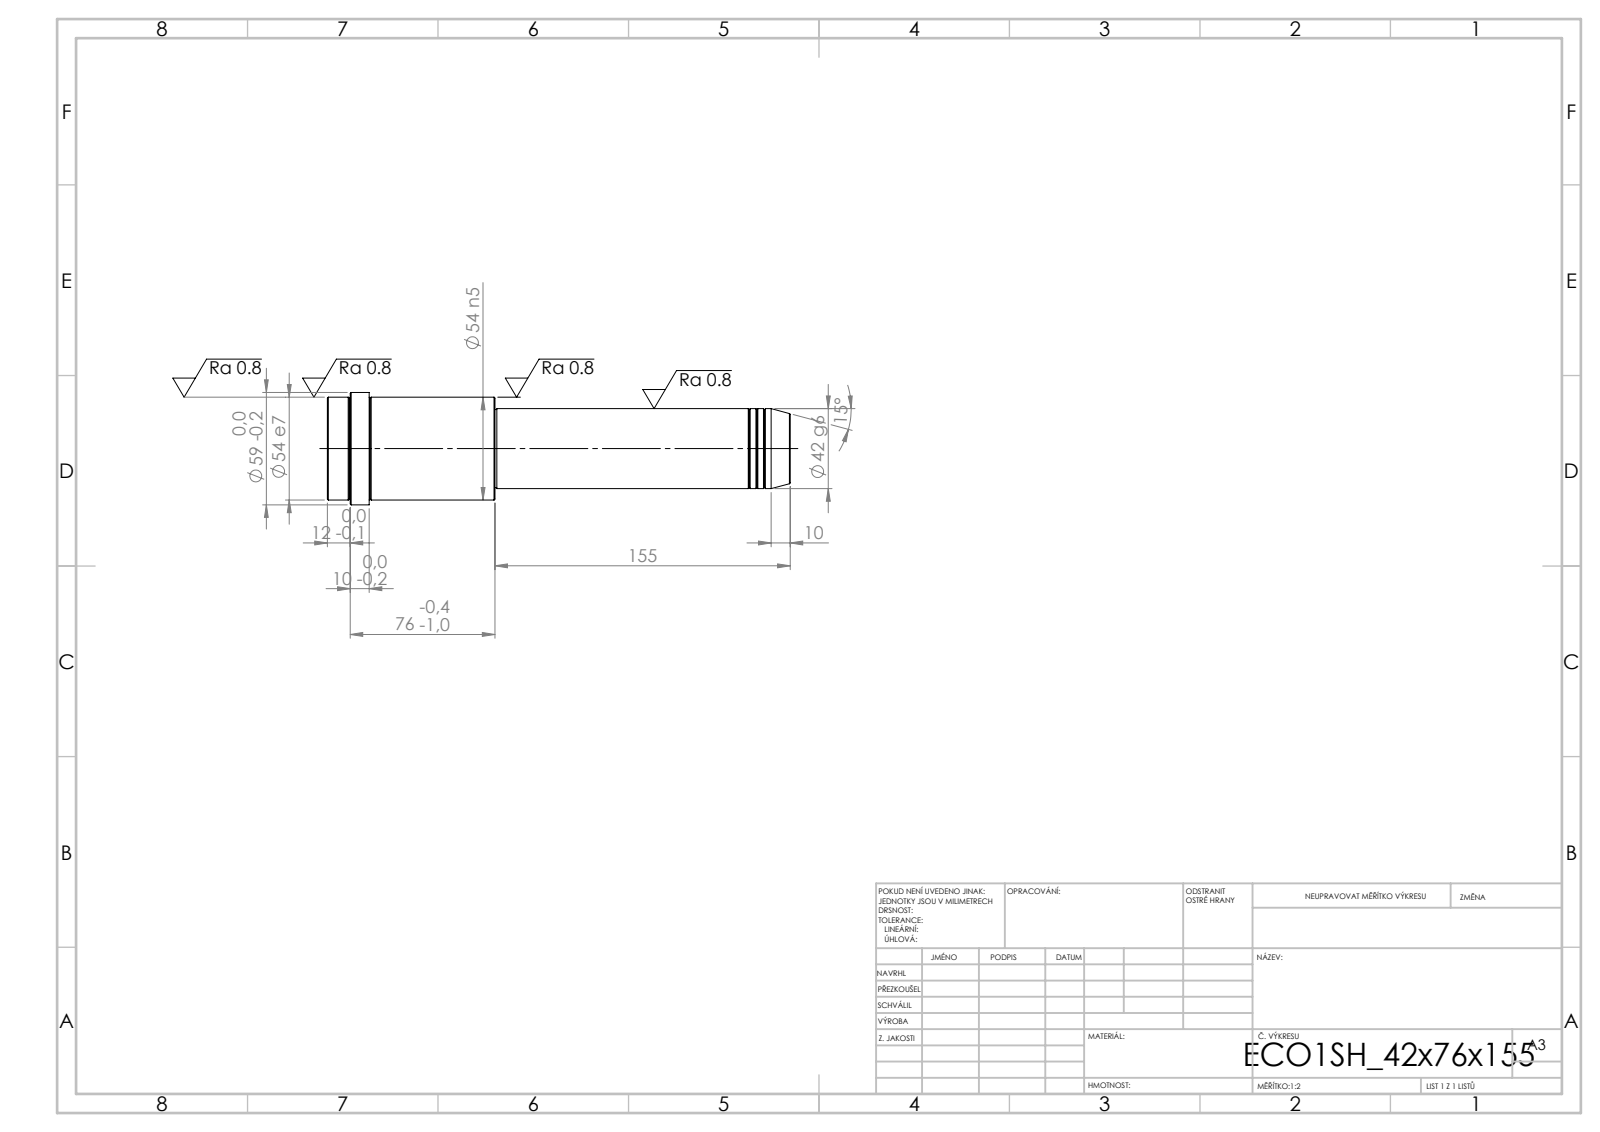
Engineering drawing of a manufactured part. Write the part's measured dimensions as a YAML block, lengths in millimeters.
step_written_by: "SolidWorks 2019 (CONFIG_CONTROL_DESIGN)"
units: millimeters
bodies: {solids: 1, faces: 52, planar: 6, cylindrical: 16, other: 30}
overall_size: [243, 59, 59]
volume: 418608
surface_area: 40997
round_bosses_or_shafts:
  - {diameter: 59, count: 1}
  - {diameter: 54, count: 1}
  - {diameter: 42, count: 1}
  - {diameter: 41, count: 1}
face_to_face_distances: [243, 155, 88, 221, 66, 22, 231, 76, 10, 12]
